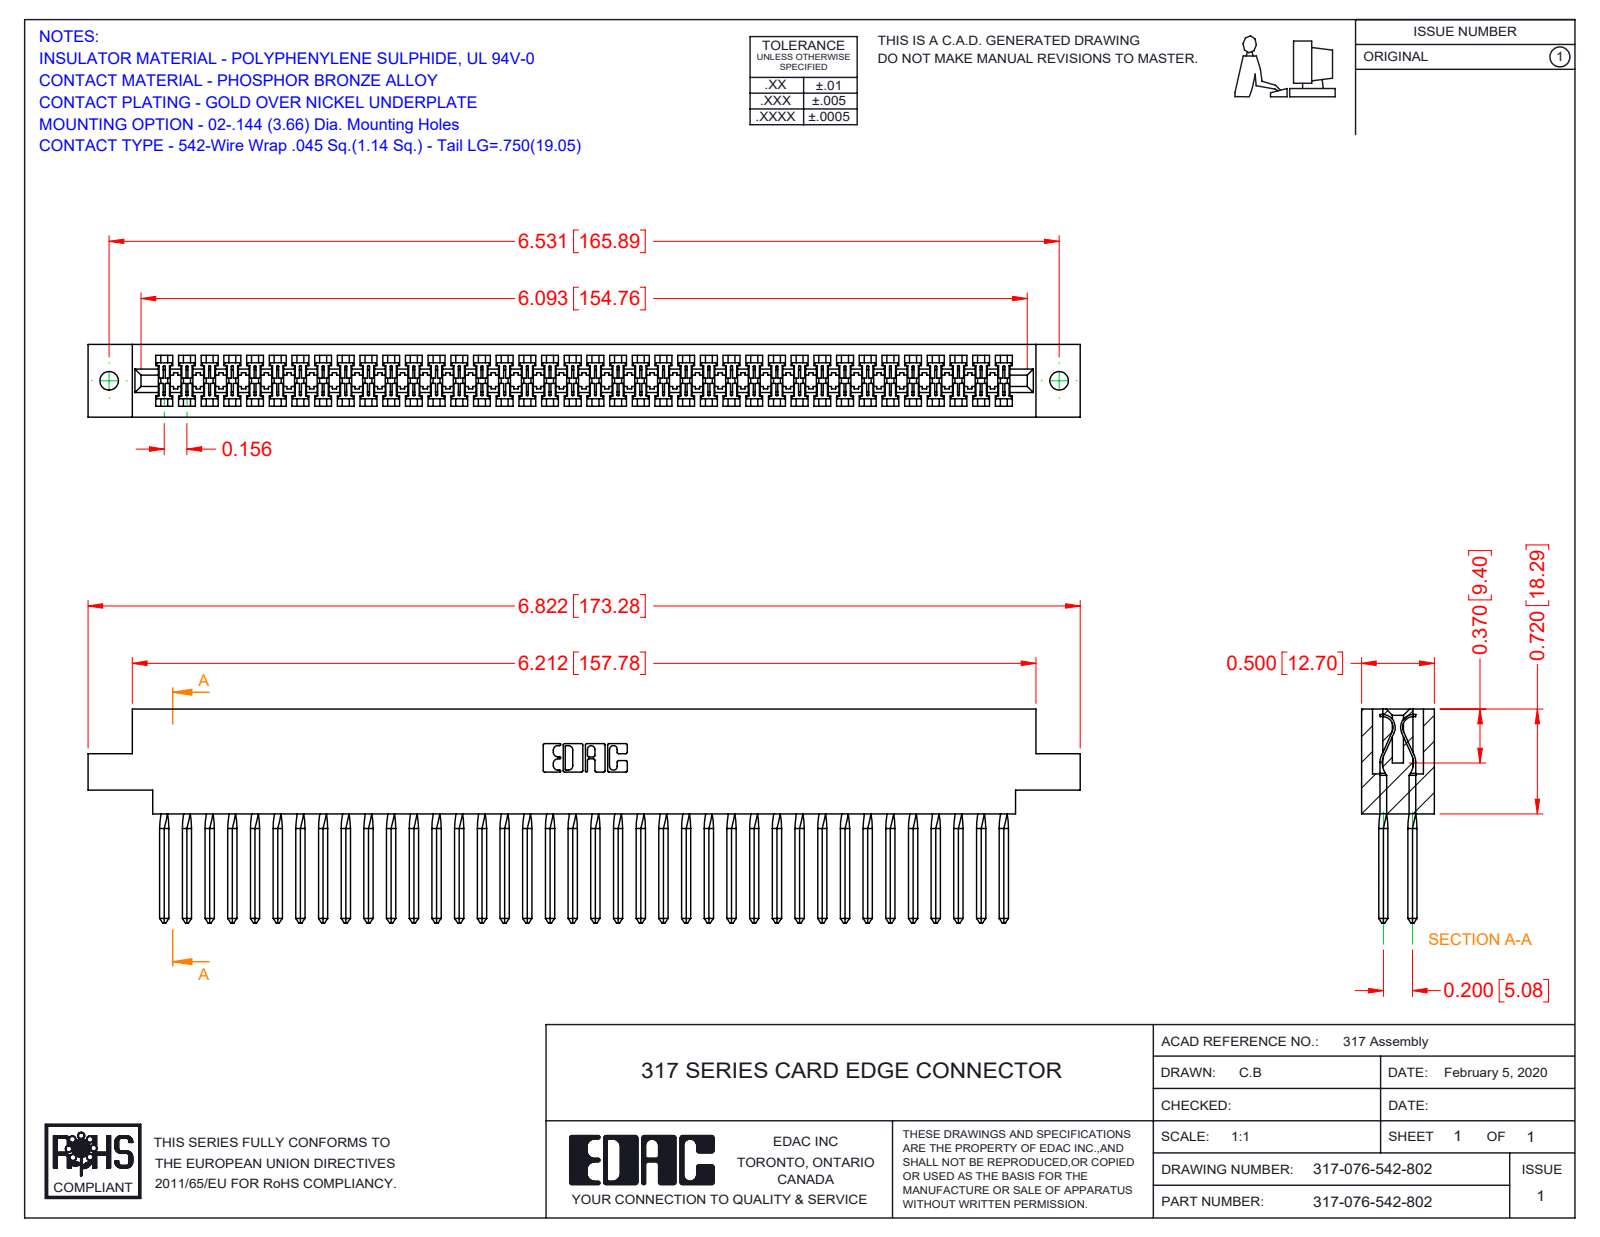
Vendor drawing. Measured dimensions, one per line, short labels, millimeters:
name: 317-076-542-802; 317-290-003_542; 317 Part_.144 Dia
written by: SolidWorks 2016 (CONFIG_CONTROL_DESIGN)
unit: mm
bodies: 77 solids, 4434 faces (3554 planar, 576 cylindrical, 304 other)
size: 173.3 × 37.3 × 12.7
volume: 28 220 mm³; area: 38 830 mm²
holes: 2× ⌀3.3
rounds: 152× R0.2, 22× R0.3, 6× R0.2, 6× R0.8, 3× R0.7, 2× R1.9, 2× R2.3, 2× R2.5
face distances: 12.7, 1.9, 10.8, 8.9, 5.1, 1.2, 3.3, 9.4, 1.3, 7.5
hole spacings: 165.9
